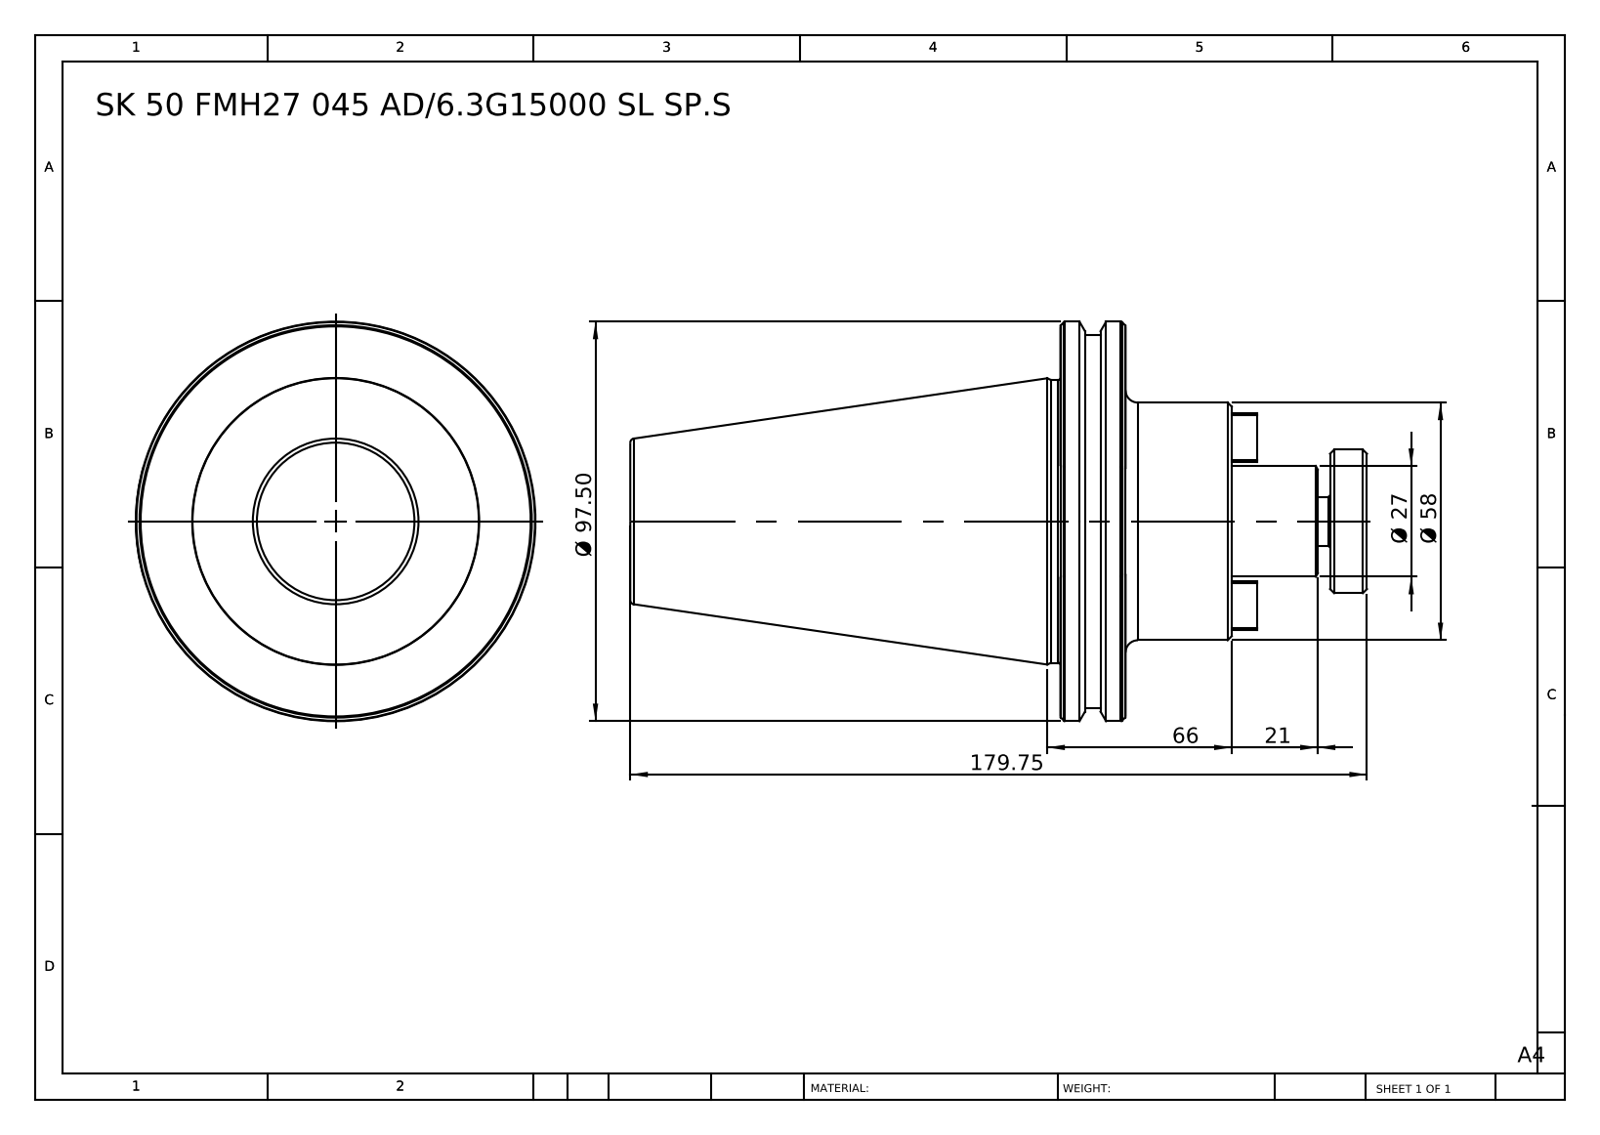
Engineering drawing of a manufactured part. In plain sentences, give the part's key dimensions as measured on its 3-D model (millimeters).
The part is named "SK50 FMH27 045 AD-6.3G15000 SL SP.S". Its 3-D file was written by "SolidWorks 2014 (CONFIG_CONTROL_DESIGN)". It is 1 solid with 99 faces: 27 planar, 16 cylindrical and 56 other. Overall it measures 179.75 by 97.5 by 97.5 millimeters. Its volume is 464 908 cubic millimeters and its surface area 45 965 square millimeters. Round bosses or shafts: 1 of diameter 97.5, 1 of diameter 91, 1 of diameter 69, 1 of diameter 58, 1 of diameter 35, 1 of diameter 27, 1 of diameter 12. The main face-to-face distances are 15.9, 25.9, 41.8, 146.75, 120.85, 104.95, 33, 58.9, 74.8, 179.75.
